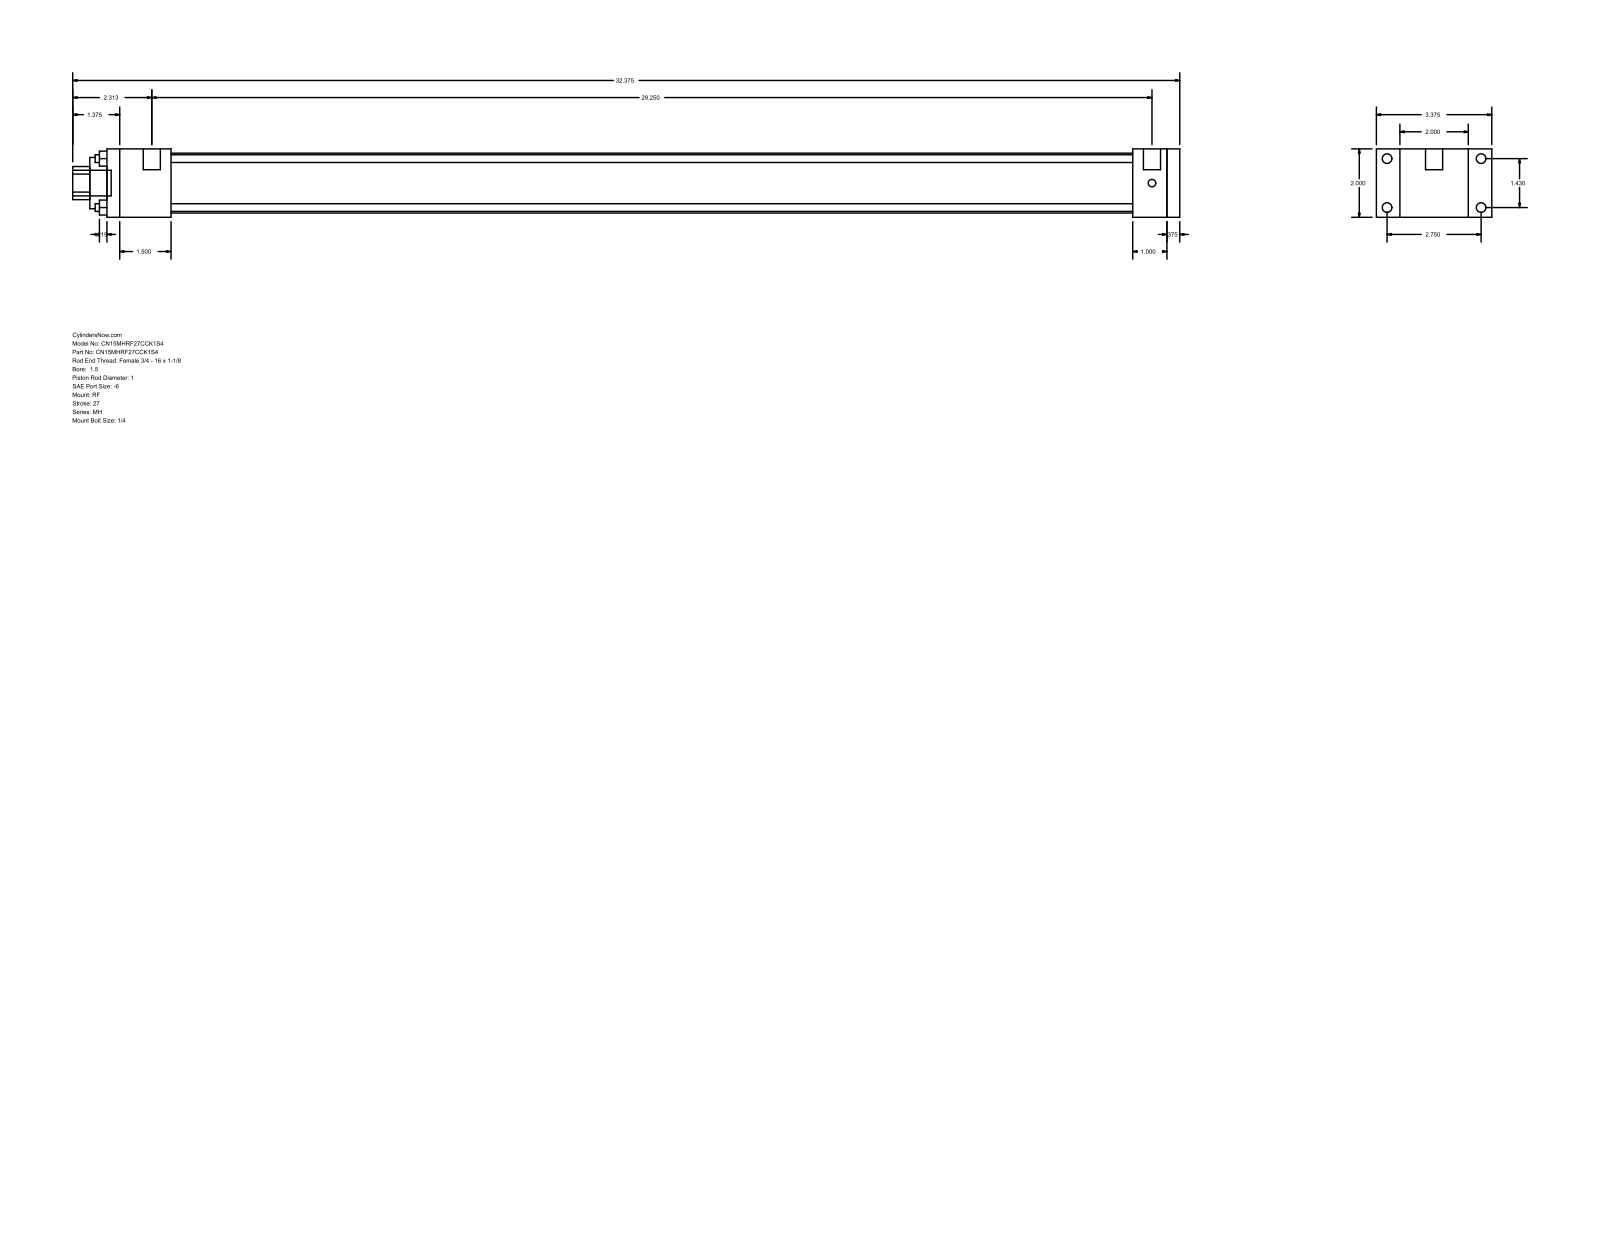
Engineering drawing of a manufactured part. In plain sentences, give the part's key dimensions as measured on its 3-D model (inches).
The part is named "MH_RF__0150_1". Its 3-D file was written by "GSSL Pune (CONFIG_CONTROL_DESIGN)". It is 0 solids with 92 faces: 64 planar, 28 cylindrical and 0 other. Overall it measures 32.375 by 3.375 by 2 inches. Round holes: 4 of diameter 0.225, 1 of diameter 1, 1 of diameter 1.5, 1 of diameter 1.75. Round bosses or shafts: 4 of diameter 0.281, 4 of diameter 0.219, 2 of diameter 0.5, 1 of diameter 0.75. Partial cylindrical surfaces (rounded edges, fillets, slot ends): 1 of radius 0.484. The main face-to-face distances are 2, 0.375, 31, 1, 31.375, 0.687, 2.687, 30, 1.375, 1.875. The hole center spacings are 1.011, 1.43, 2.022.
